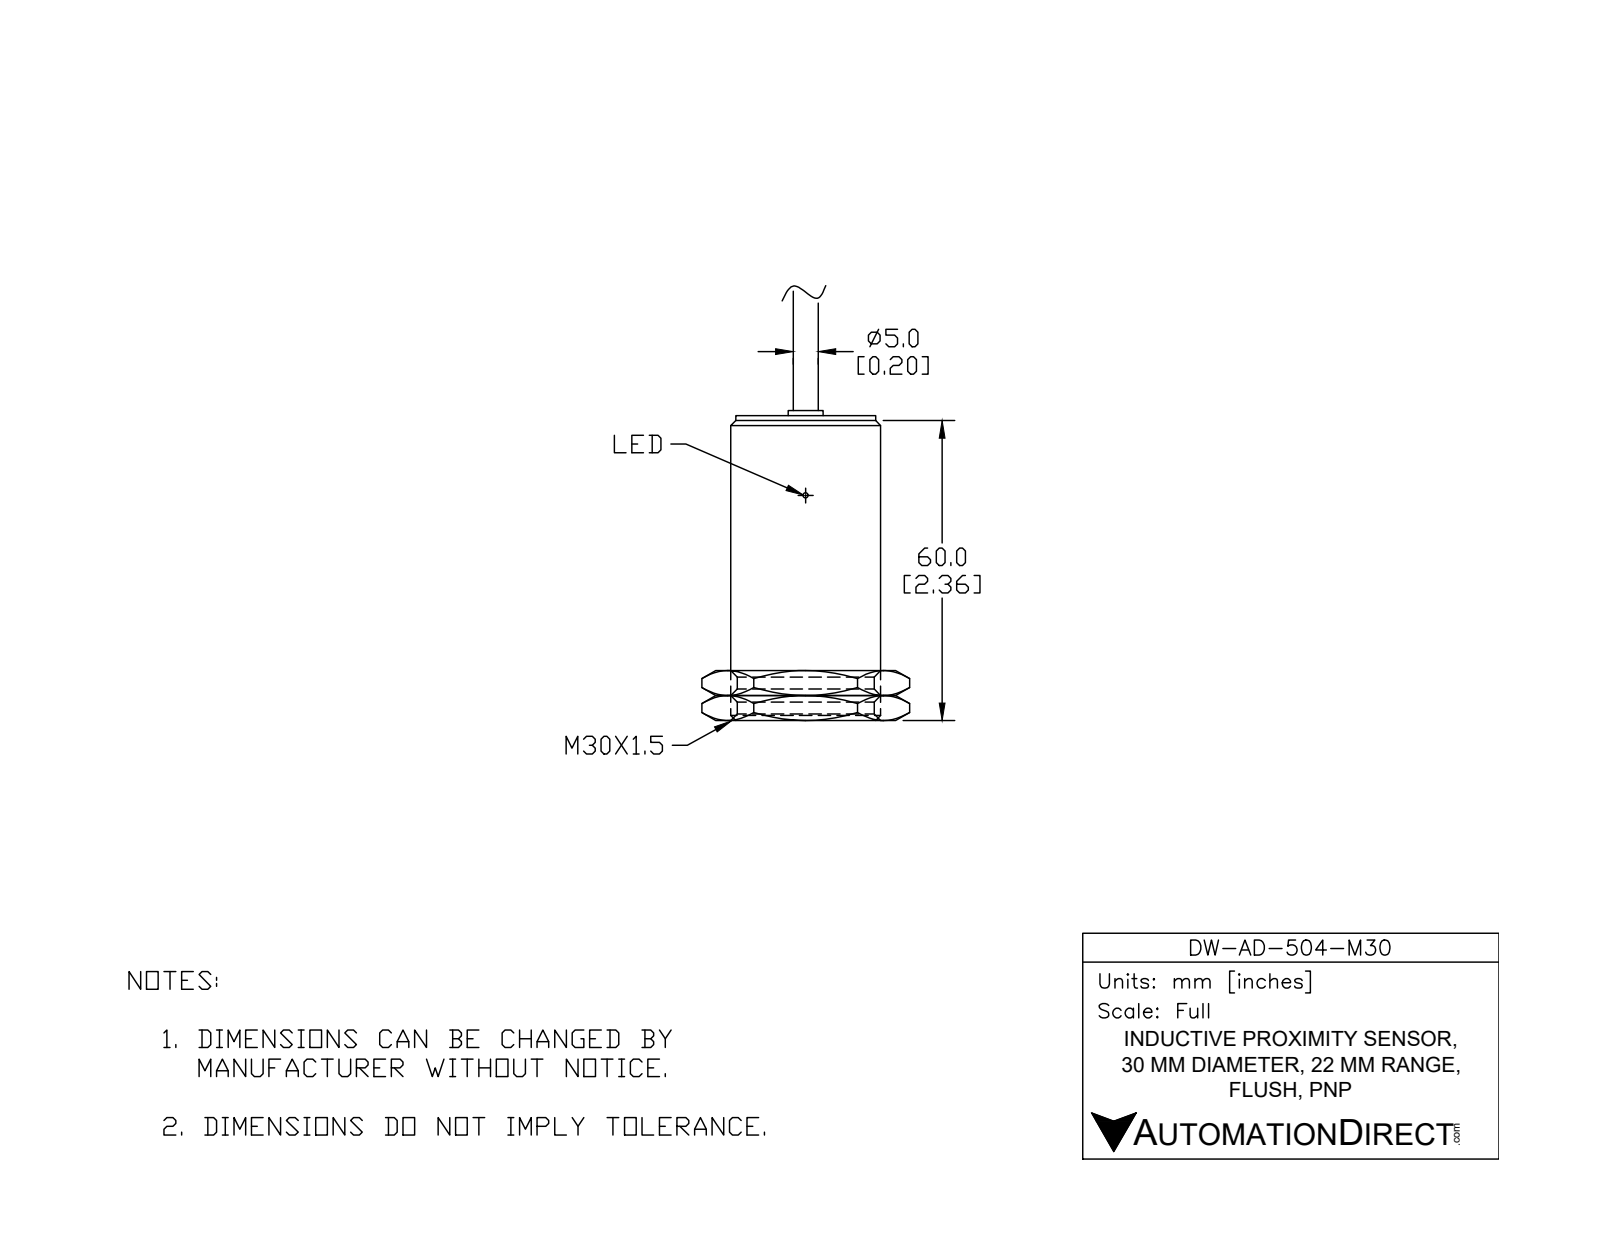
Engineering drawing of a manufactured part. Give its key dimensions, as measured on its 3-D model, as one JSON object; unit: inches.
{"part_name": "DW-AD-504-M30", "step_written_by": "SolidWorks 2017 (AUTOMOTIVE_DESIGN)", "units": "inches", "bodies": {"solids": 2, "faces": 31, "planar": 17, "cylindrical": 5, "other": 9}, "overall_size": [3.409, 1.181, 1.181], "volume_in3": 2.658, "surface_area_in2": 11.68, "round_bosses_or_shafts": [[1.181, 1], [1.083, 1], [0.413, 1], [0.268, 1], [0.197, 1]], "face_to_face_distances": [2.402, 2.48, 0.079, 0.031, 2.433, 0.047, 2.283, 0.118, 0.15, 0.197]}
